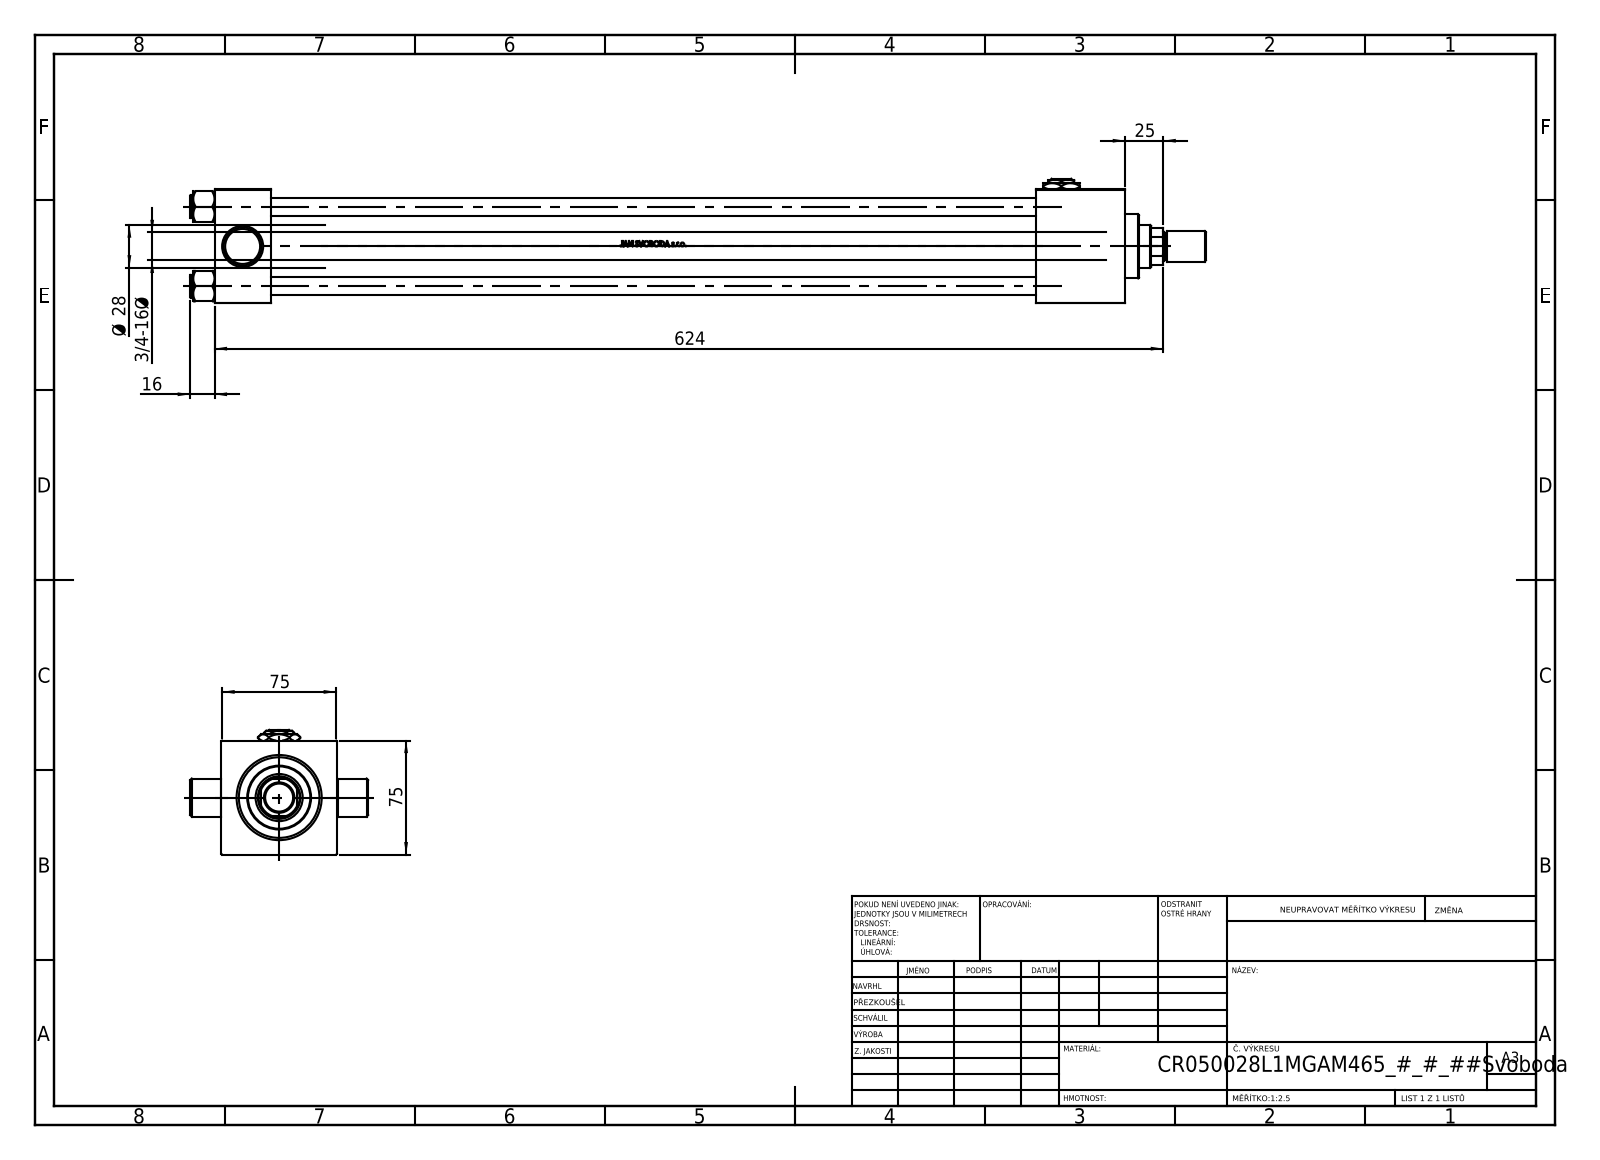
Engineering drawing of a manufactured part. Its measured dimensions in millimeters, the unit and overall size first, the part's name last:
Units: millimetres
Overall size (bounding box): 668 × 117 × 82
Round holes (diameter × count): ⌀12 ×4, ⌀7 ×2, ⌀20.96 ×2, ⌀30 ×2, ⌀18.5 ×1, ⌀28 ×1, ⌀31 ×1, ⌀41 ×1, ⌀50 ×1, ⌀53 ×1
Round bosses / shafts (diameter × count): ⌀15 ×4, ⌀56 ×1, ⌀42 ×1, ⌀25 ×1, ⌀20 ×1, ⌀18 ×1
Partial cylindrical surfaces — rounded edges, fillets, slot ends (radius × count): R13.5 ×1
Main face-to-face distances: 75, 37, 0.5, 76, 75.5, 599, 562, 59, 540, 503
Hole centre spacings: 36.98, 52.3, 73.96, 538.5
Volume: 1 405 000 mm³ · Surface area: 408 057 mm²
Bodies: 13 solids, 1133 faces (455 planar, 128 cylindrical, 550 other)
Part name (STEP PRODUCT): V215CR_L_TYCINKA; V215CR_VCP_L; V215CR_L_Body; V215_VC_A (+3 more)
STEP written by: SolidWorks 2019 (CONFIG_CONTROL_DESIGN)
